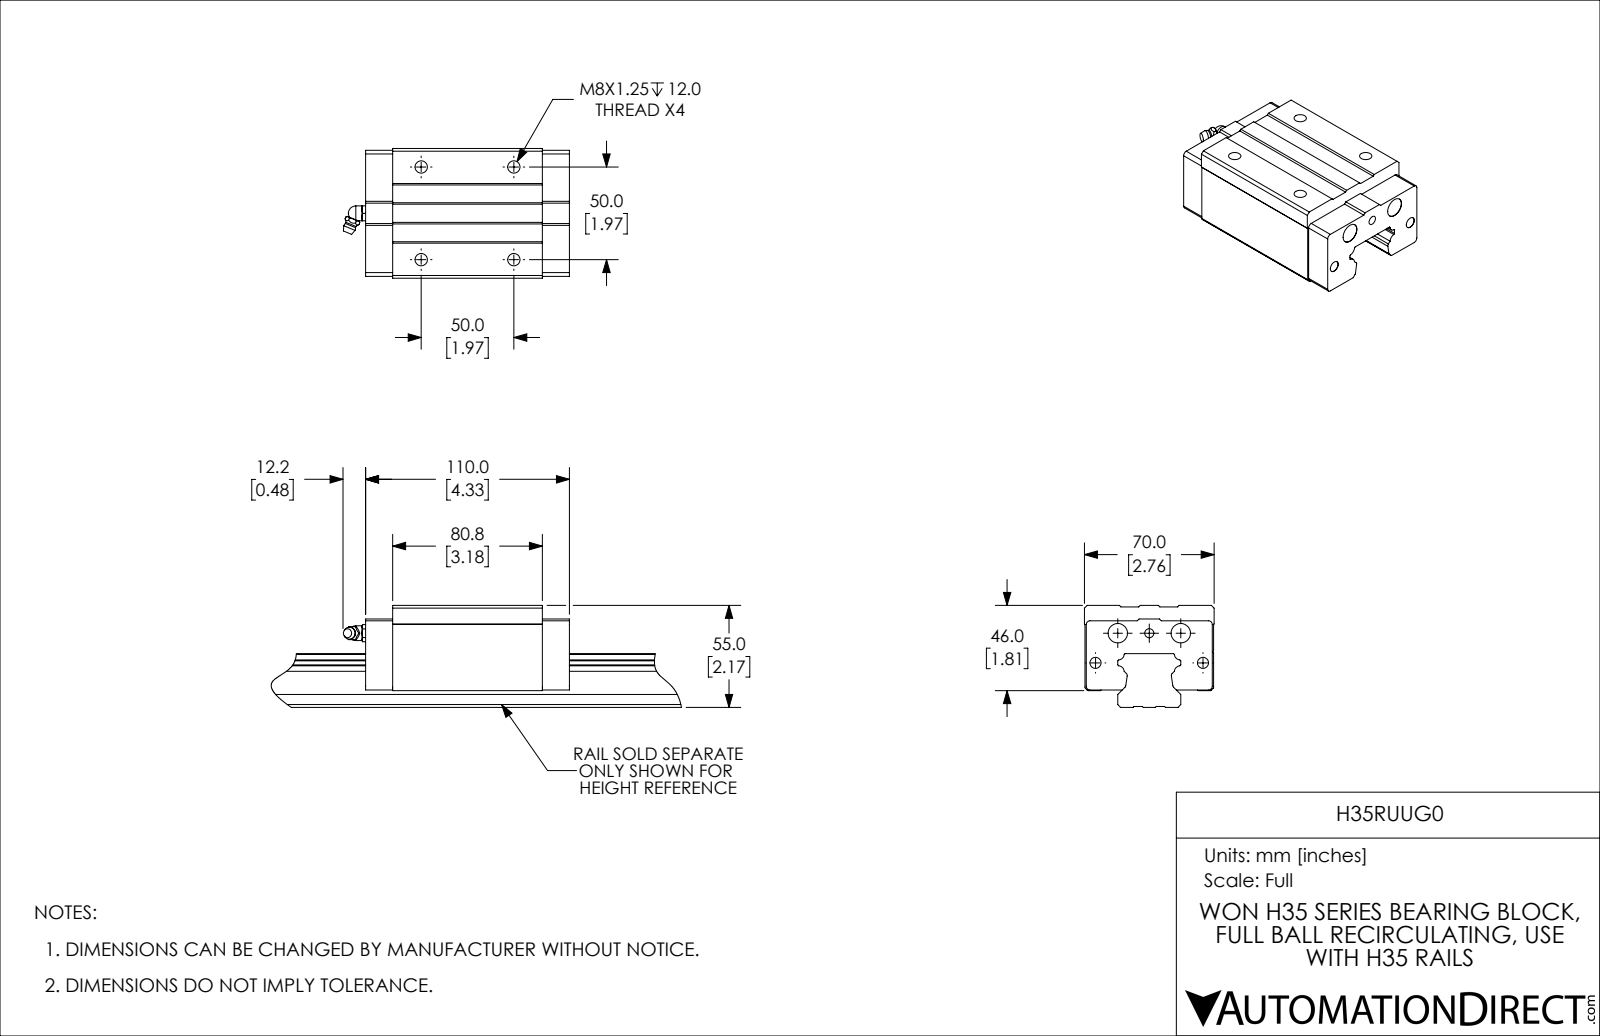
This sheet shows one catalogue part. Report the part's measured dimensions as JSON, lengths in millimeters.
{"part_name": "H35RUUG0", "step_written_by": "SolidWorks 2019 (CONFIG_CONTROL_DESIGN)", "units": "millimeters", "bodies": {"solids": 2, "faces": 170, "planar": 85, "cylindrical": 55, "other": 30}, "overall_size": [122, 70, 46], "volume_mm3": 268414, "surface_area_mm2": 36789, "round_holes": [[6.65, 4], [6, 2], [10.5, 2], [4.92, 1]], "round_bosses_or_shafts": [[8, 1], [6, 1]], "partial_cylinders_radius": [[1, 4], [1.5, 4], [2, 4], [3.2, 4], [0.5, 2], [1.3, 1]], "face_to_face_distances": [45.6, 26, 19.6, 69.4, 17.7, 0.7, 68.7, 110, 1, 44.8], "hole_center_spacings": [50, 17, 20, 33.12, 48.7, 70.71, 34, 58]}
